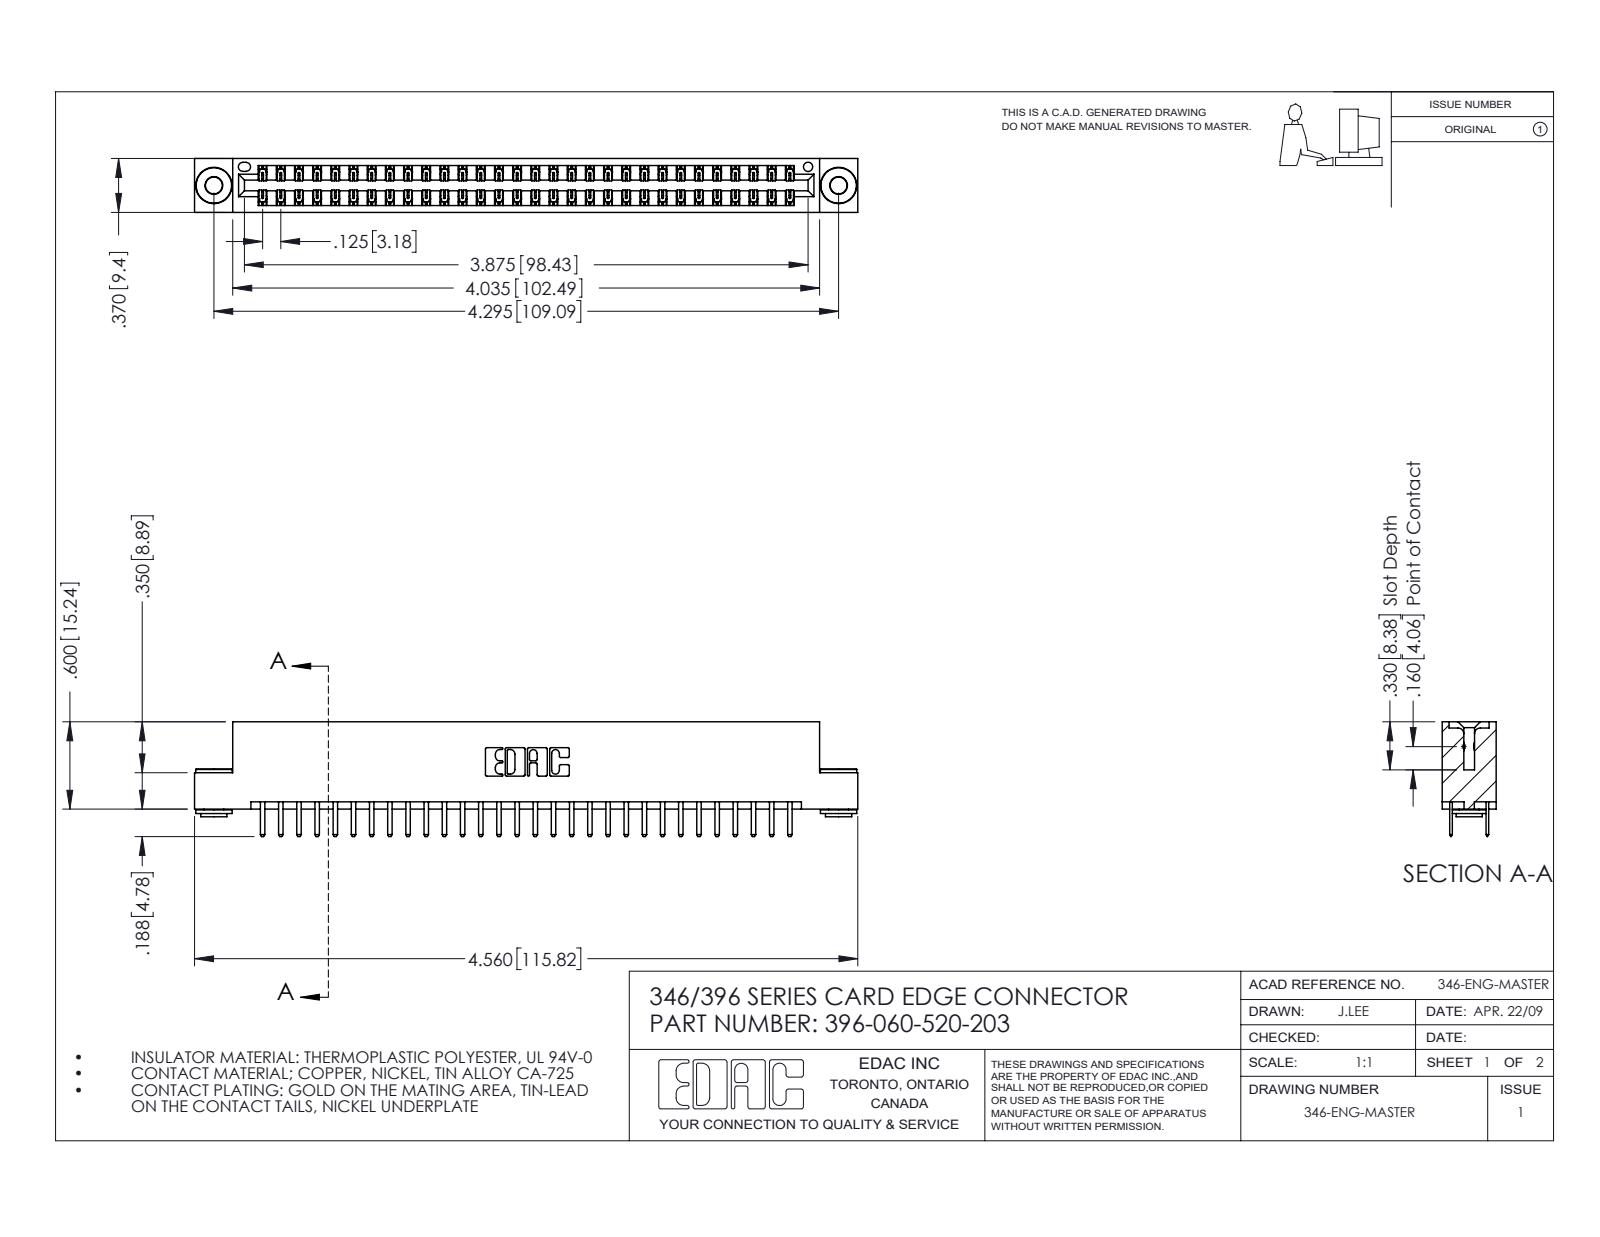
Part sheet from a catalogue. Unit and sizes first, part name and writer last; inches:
Units: inches
Overall size (bounding box): 4.56 × 0.788 × 0.37
Round holes (diameter × count): ⌀0.116 ×2, ⌀0.156 ×2, ⌀0.064 ×1
Round bosses / shafts (diameter × count): ⌀0.25 ×2, ⌀0.18 ×2, ⌀0.136 ×2
Partial cylindrical surfaces — rounded edges, fillets, slot ends (radius × count): R0.006 ×90, R0.01 ×64, R0.01 ×22, R0.007 ×6, R0.031 ×6, R0.026 ×3, R0.014 ×2, R0.022 ×2
Main face-to-face distances: 0.048, 0.322, 0.25, 0.37, 0.025, 0.275, 0.072, 0.298, 0.148, 0.222
Hole centre spacings: 0.246, 4.087, 4.295
Volume: 0.683 in³ · Surface area: 23.79 in²
Bodies: 63 solids, 3520 faces (2306 planar, 1206 cylindrical, 8 other)
Part name (STEP PRODUCT): 345-292-001_345-293-120; 346 Part_Flush Mounting Lugs - 0.156 Dia-TH; 396-060-520-203; 345-250-002_345-250-002-102
STEP written by: SolidWorks 2016 (CONFIG_CONTROL_DESIGN)
